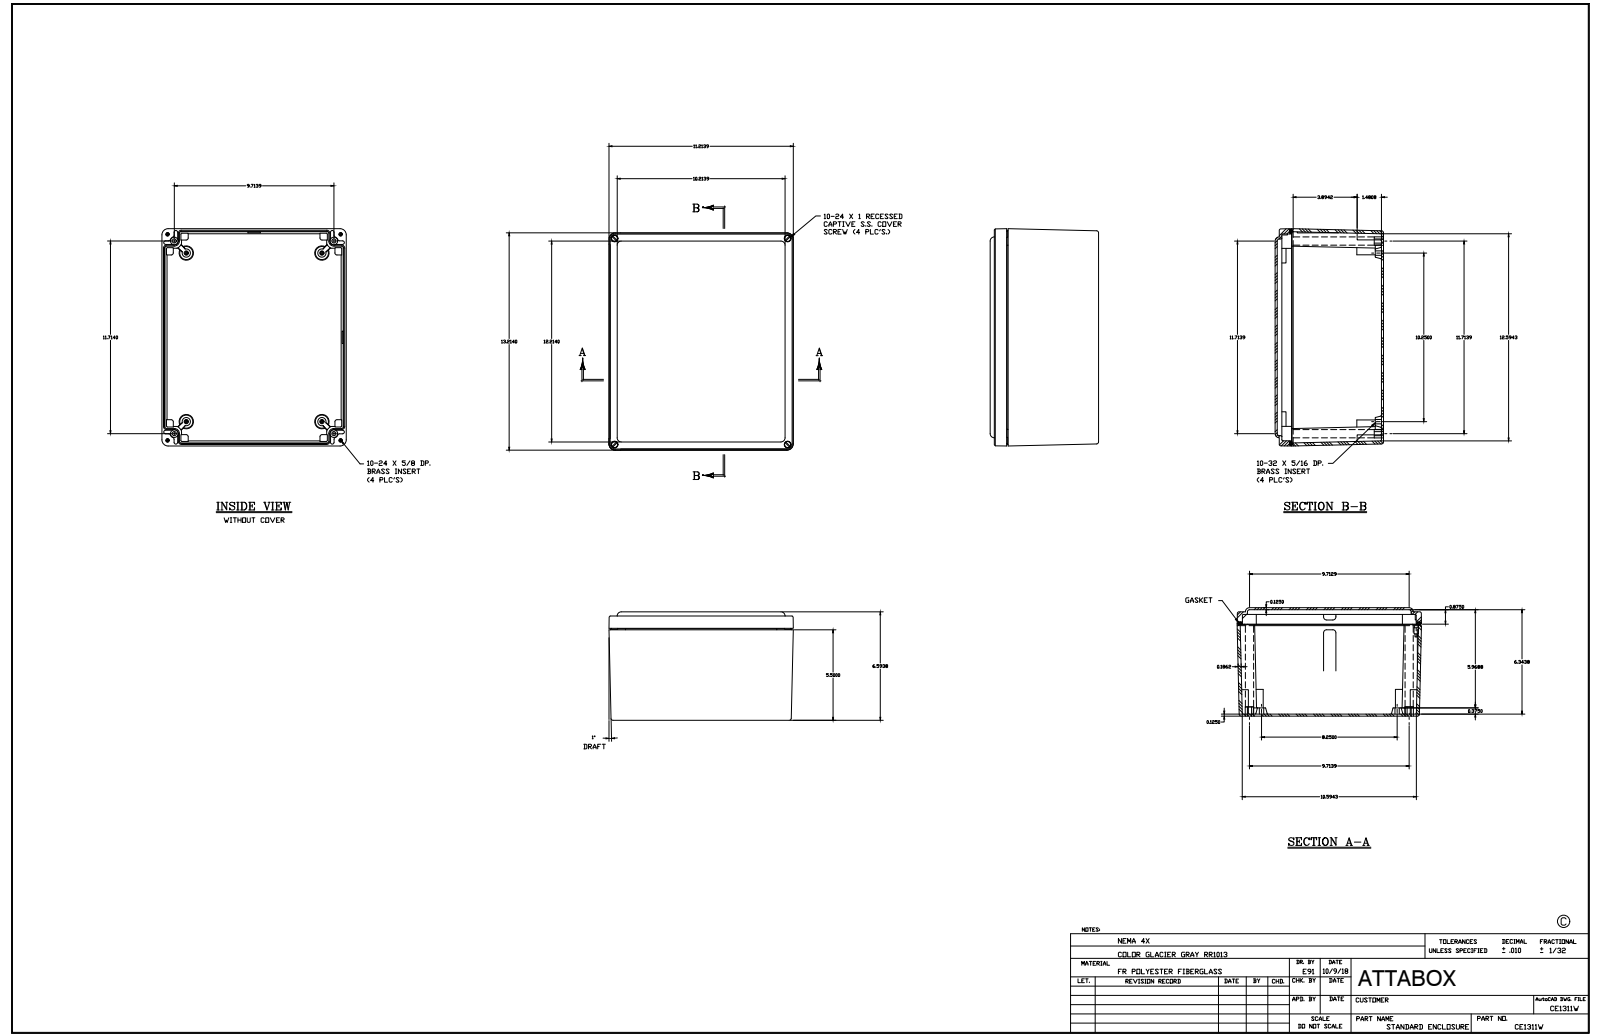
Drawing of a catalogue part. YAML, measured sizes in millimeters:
part_name: "CE1311W"
step_written_by: "SolidWorks 2018 (AUTOMOTIVE_DESIGN)"
units: millimeters
bodies: {solids: 23, faces: 1101, planar: 437, cylindrical: 296, other: 368}
overall_size: [335.8, 285, 167.5]
volume: 1791000
surface_area: 835500
round_holes:
  - {diameter: 7.1, count: 8}
  - {diameter: 4, count: 4}
  - {diameter: 4, count: 4}
  - {diameter: 4.8, count: 4}
  - {diameter: 5.6, count: 4}
  - {diameter: 5.8, count: 4}
  - {diameter: 7.1, count: 4}
  - {diameter: 8, count: 4}
  - {diameter: 10.3, count: 4}
  - {diameter: 13.5, count: 4}
  - {diameter: 3.7, count: 3}
  - {diameter: 3.7, count: 1}
round_bosses_or_shafts:
  - {diameter: 9.5, count: 4}
  - {diameter: 9.2, count: 4}
  - {diameter: 4.9, count: 4}
partial_cylinders:
  - {radius: 0.8, count: 57}
  - {radius: 3.2, count: 38}
  - {radius: 1.6, count: 26}
  - {radius: 0.3, count: 16}
  - {radius: 1.5, count: 8}
  - {radius: 4.8, count: 8}
  - {radius: 6.4, count: 8}
  - {radius: 9.5, count: 8}
face_to_face_distances: [4.7, 3.2, 161.1, 167.5, 164.3, 164.3, 3.2, 6.4, 158, 19.1]
hole_center_spacings: [14.6, 14.6, 26.4, 41, 41, 229, 240.3, 240.3]
